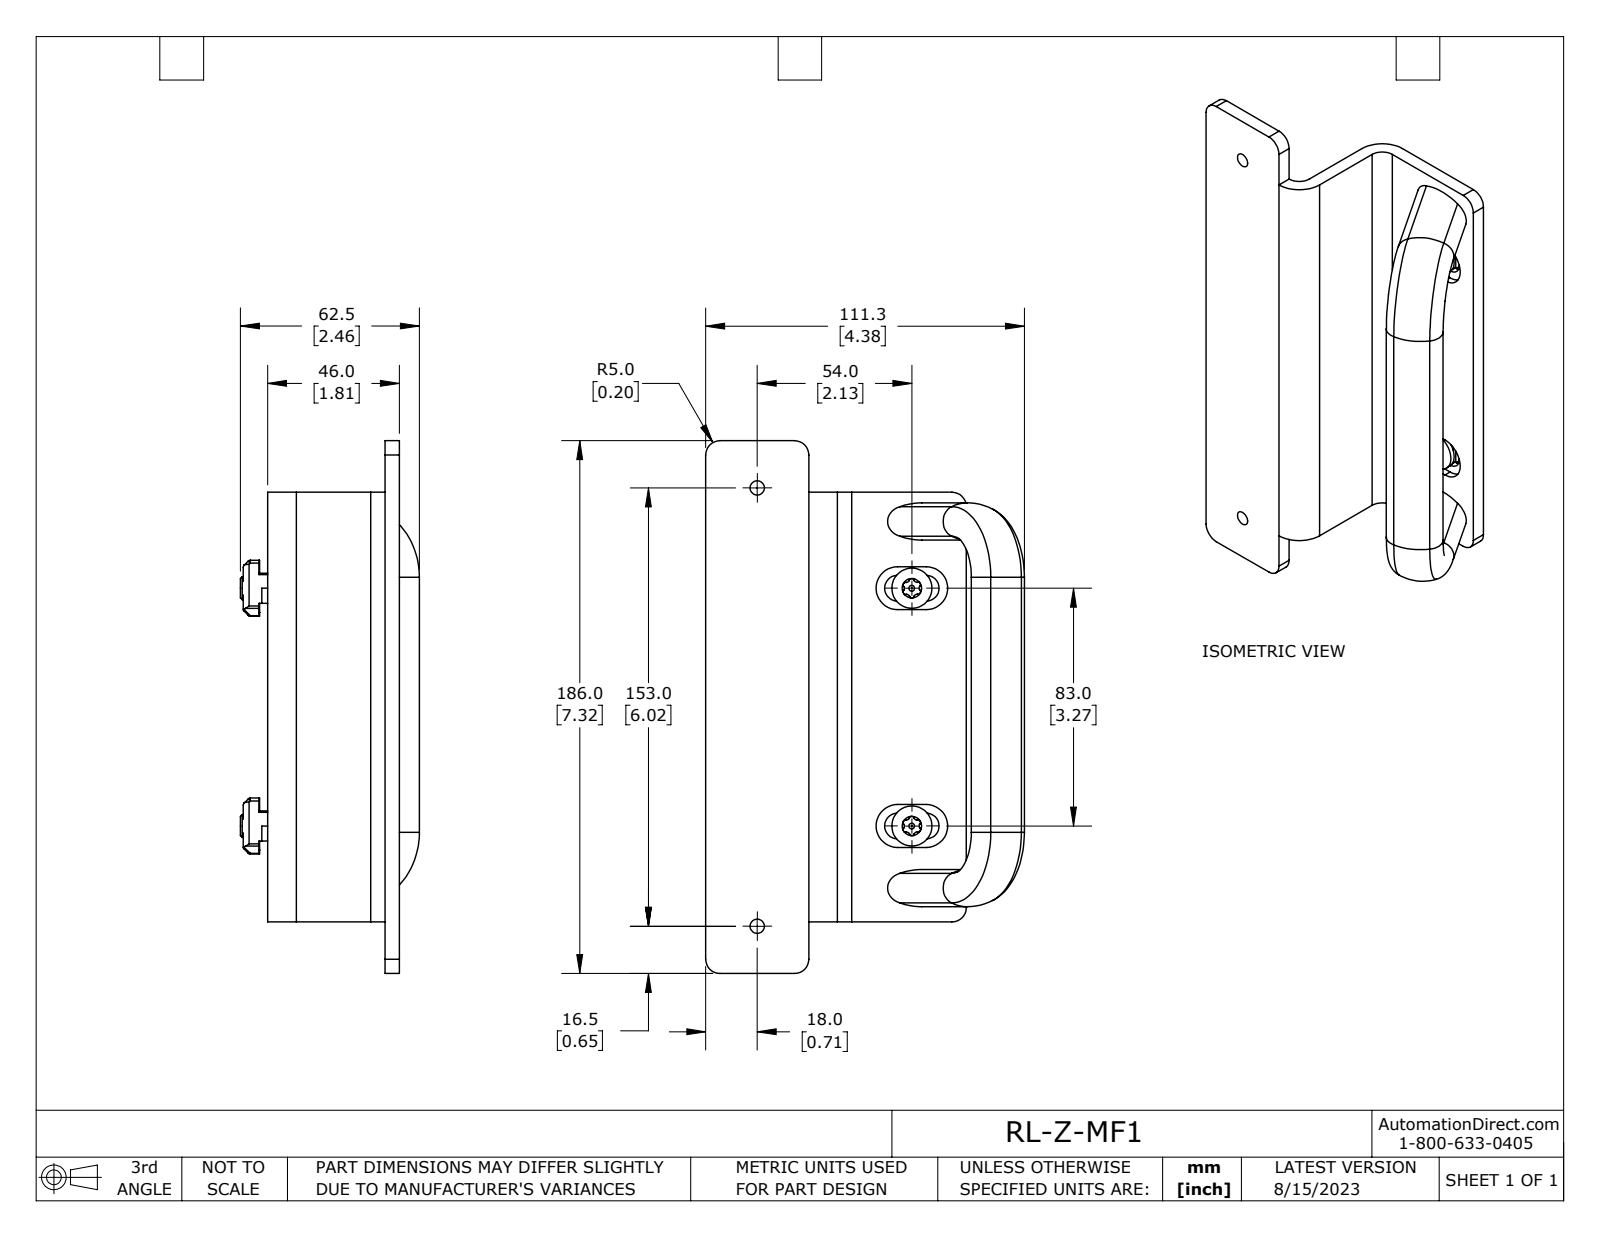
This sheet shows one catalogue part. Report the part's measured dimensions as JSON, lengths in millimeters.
{"part_name": "RL-Z-MF1_REV1", "step_written_by": "SolidWorks 2021 (AUTOMOTIVE_DESIGN)", "units": "millimeters", "bodies": {"solids": 8, "faces": 336, "planar": 138, "cylindrical": 164, "other": 34}, "overall_size": [186, 111.3, 62.5], "volume_mm3": 145900, "surface_area_mm2": 59940, "round_holes": [[5, 4], [4.9, 2], [6.8, 2]], "round_bosses_or_shafts": [[8, 4], [15.2, 2], [14, 2], [2, 2]], "partial_cylinders_radius": [[0.3, 48], [1, 30], [1.4, 24], [5, 8], [5.5, 6], [16.2, 6], [0.5, 4], [4.5, 4]], "face_to_face_distances": [5, 41, 46, 36, 2.5, 91, 50, 45, 38.5, 43.5], "hole_center_spacings": [64.3, 129.8, 22.3, 23.8, 60.1, 60.5, 83, 104.8]}
